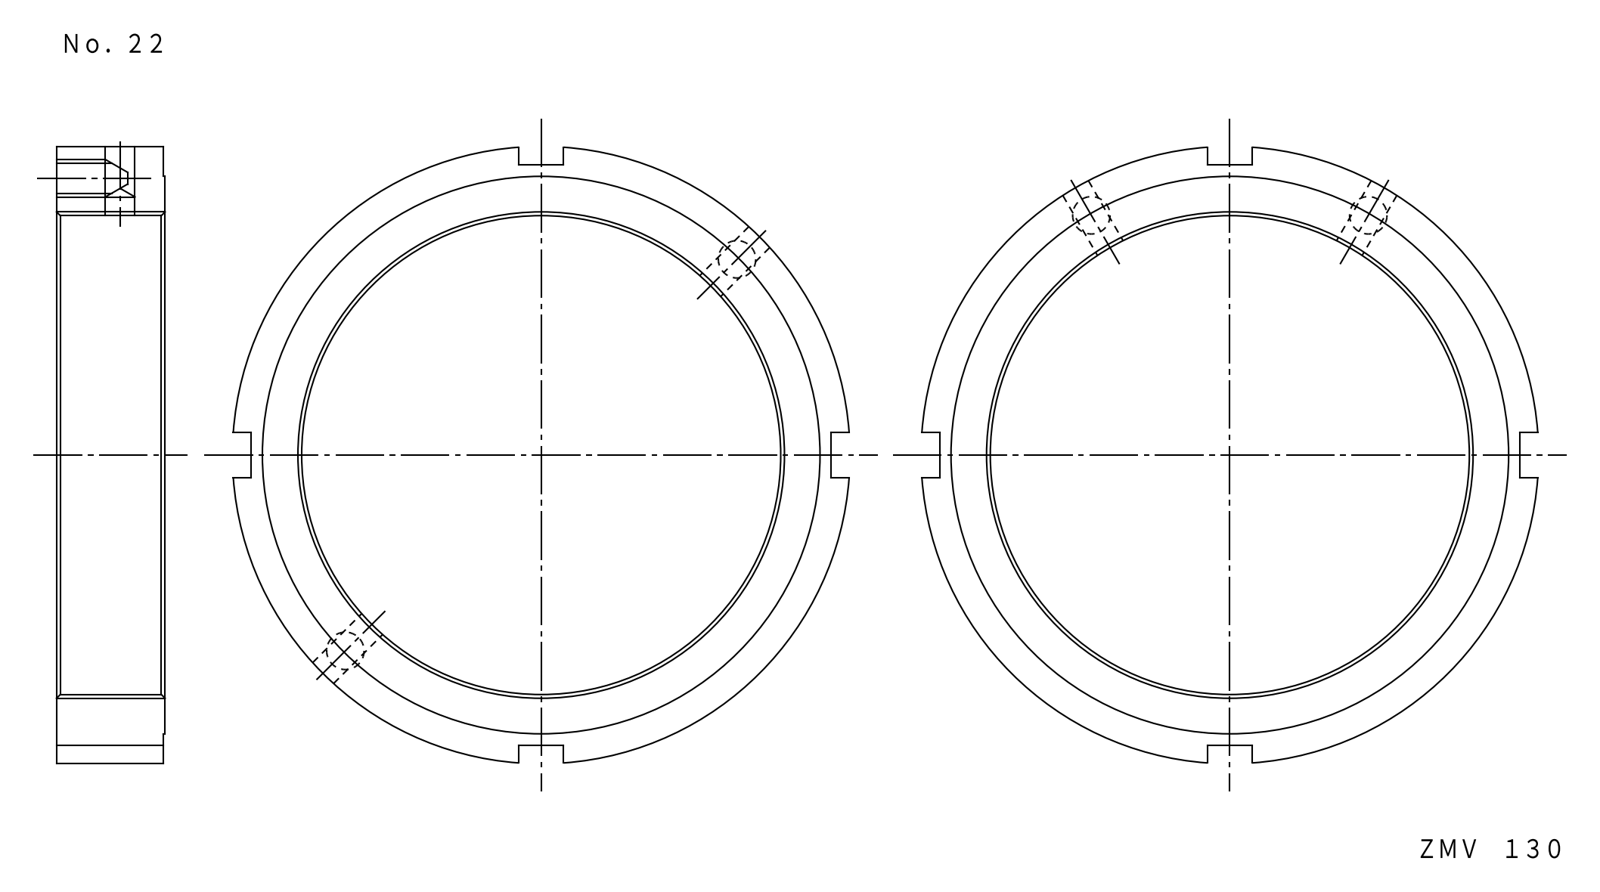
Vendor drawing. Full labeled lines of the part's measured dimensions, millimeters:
Part name (STEP PRODUCT): FKD ZMV130
STEP written by: Autodesk Inventor LT (CONFIG_CONTROL_DESIGN)
Units: millimetres
Bodies: 1 solid, 29 faces (15 planar, 10 cylindrical, 4 other)
Overall size (bounding box): 164.56 × 164.56 × 29
Volume: 223 225 mm³ · Surface area: 44 881 mm²
Round holes (diameter × count): ⌀7.9 ×2, ⌀8.38 ×2, ⌀130 ×1
Round bosses / shafts (diameter × count): ⌀165 ×1, ⌀149 ×1
Main face-to-face distances: 29, 0.5, 28.5, 71.5, 83.5, 155, 12
Hole centre spacings: 74.01, 148.01
